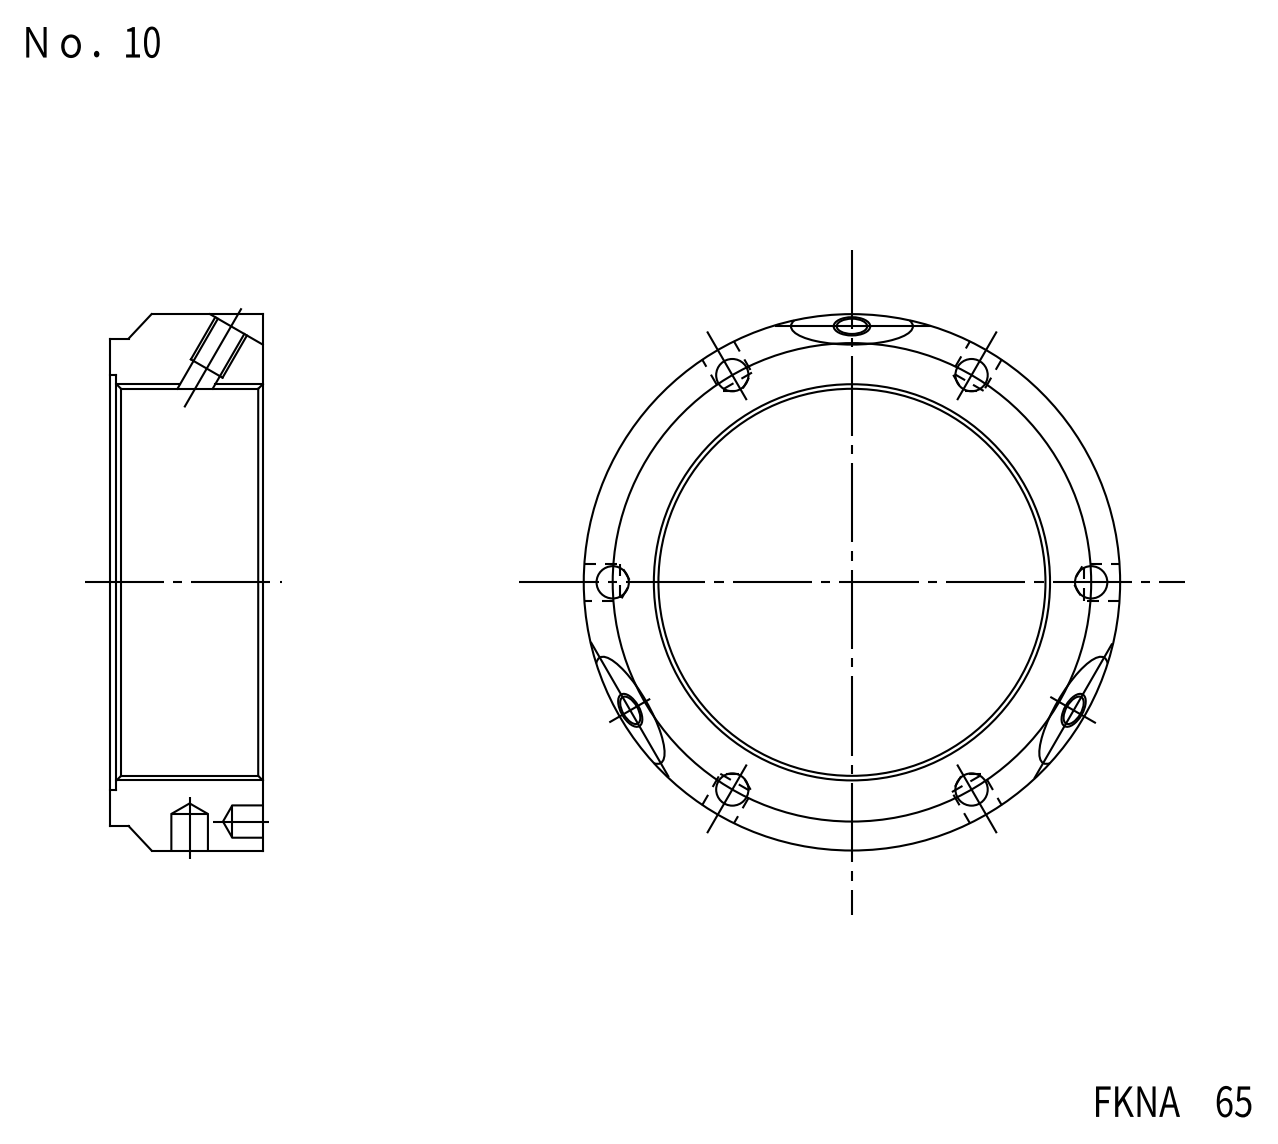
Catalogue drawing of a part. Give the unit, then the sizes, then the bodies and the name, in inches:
Units: inches
Overall size (bounding box): 3.465 × 3.465 × 0.984
Round holes (diameter × count): ⌀0.209 ×6, ⌀0.236 ×3, ⌀0.24 ×3, ⌀0.194 ×2, ⌀0.194 ×1, ⌀2.559 ×1, ⌀2.677 ×1
Round bosses / shafts (diameter × count): ⌀3.465 ×1, ⌀3.15 ×1
Partial cylindrical surfaces — rounded edges, fillets, slot ends (radius × count): R0.787 ×3
Main face-to-face distances: 0.984, 0.059, 0.925
Hole centre spacings: 1.545, 2.676, 2.677, 3.091, 1.546
Volume: 3.865 in³ · Surface area: 28.86 in²
Bodies: 1 solid, 44 faces (6 planar, 25 cylindrical, 13 other)
Part name (STEP PRODUCT): FKD FKNA65
STEP written by: Autodesk Inventor LT (CONFIG_CONTROL_DESIGN)
